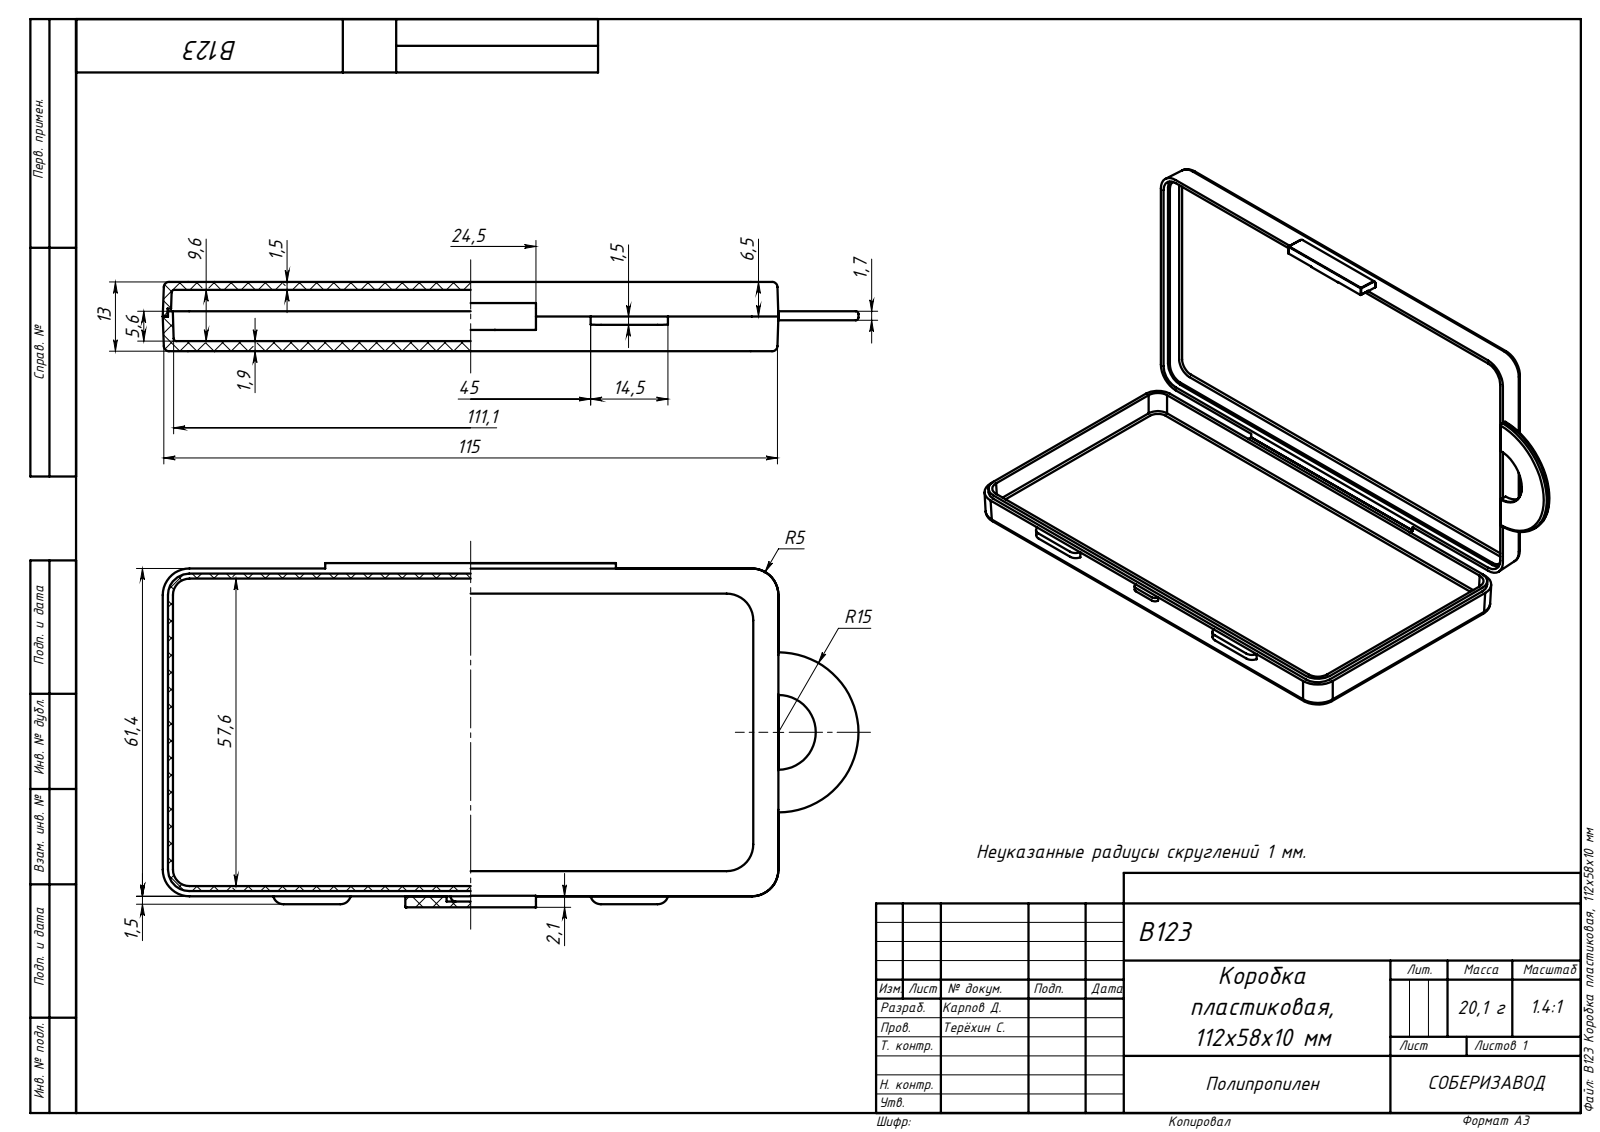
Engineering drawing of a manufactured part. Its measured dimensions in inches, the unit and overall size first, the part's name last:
Units: inches
Overall size (bounding box): 5.135 × 2.54 × 0.512
Partial cylindrical surfaces — rounded edges, fillets, slot ends (radius × count): R0.197 ×12, R0.039 ×11, R0.004 ×9, R0.02 ×8, R0.079 ×4, R0.122 ×4, R0.138 ×4, R0.276 ×1
Main face-to-face distances: 0.378, 0.055, 0.433, 0.071, 0.449, 0.504, 0.075, 0.059, 0.508, 0.256
Volume: 1.764 in³ · Surface area: 57.73 in²
Bodies: 3 solids, 176 faces (76 planar, 59 cylindrical, 41 other)
Part name (STEP PRODUCT): B123 Емкость; B123 Коробка пластиковая, 112x58x10 мм; B123 Крышка
STEP written by: SolidWorks 2020 (AUTOMOTIVE_DESIGN)
